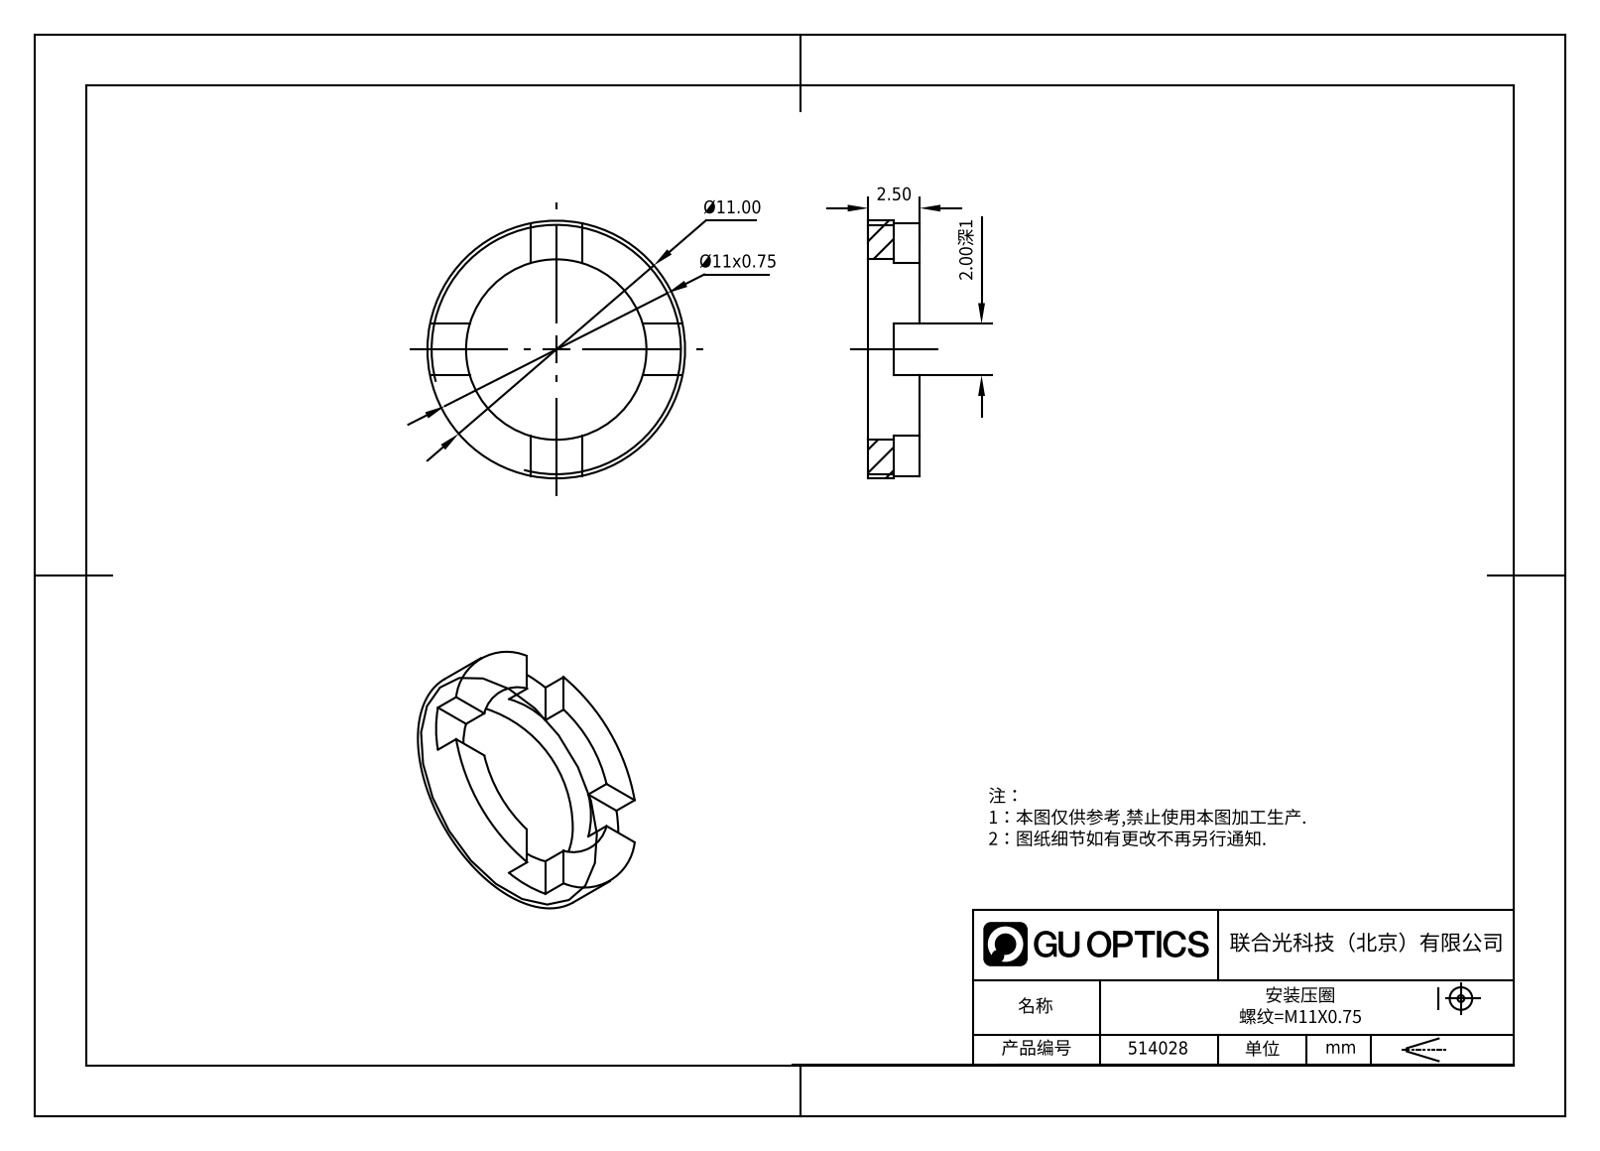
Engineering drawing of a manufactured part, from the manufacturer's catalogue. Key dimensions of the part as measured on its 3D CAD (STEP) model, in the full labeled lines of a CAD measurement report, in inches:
Part name (STEP PRODUCT): 514028
STEP written by: SolidWorks 2020 (CONFIG_CONTROL_DESIGN)
Units: inches
Bodies: 1 solid, 21 faces (17 planar, 4 cylindrical, 0 other)
Overall size (bounding box): 0.433 × 0.433 × 0.098
Volume: 0.006 in³ · Surface area: 0.364 in²
Round holes (diameter × count): ⌀0.315 ×1
Round bosses / shafts (diameter × count): ⌀0.433 ×1
Main face-to-face distances: 0.098, 0.059, 0.039, 0.079
